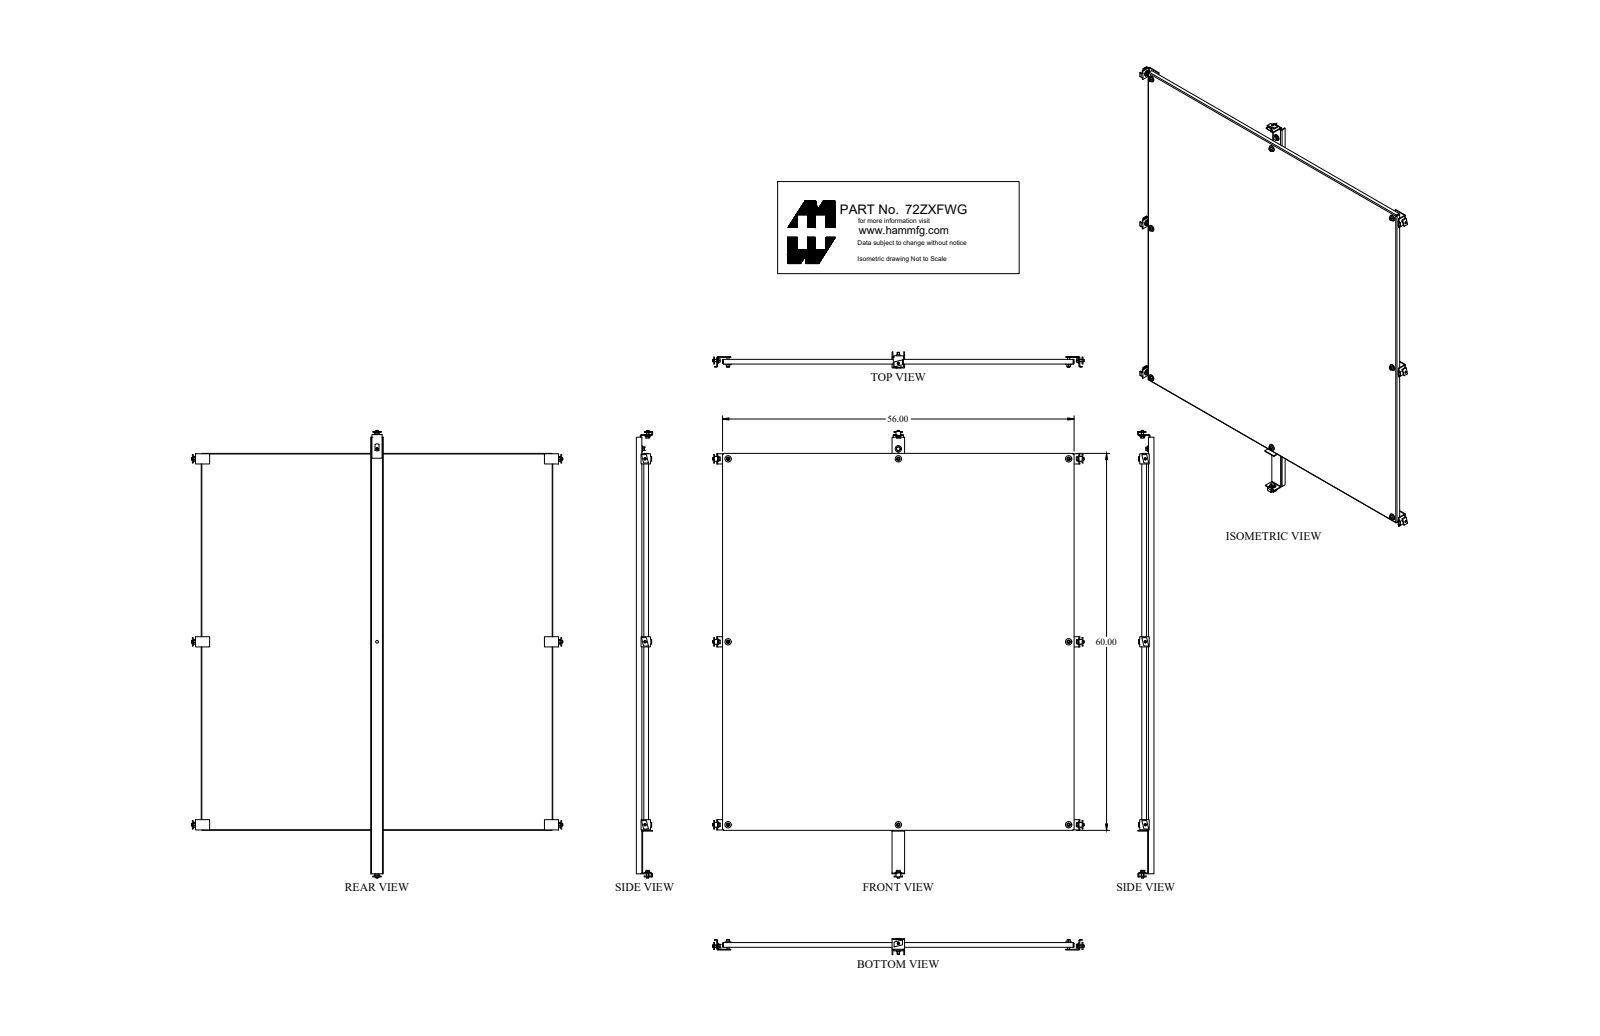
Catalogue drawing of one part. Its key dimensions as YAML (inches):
part_name: "72ZXFWG_Default"
step_written_by: "SolidWorks 2018 (CONFIG_CONTROL_DESIGN)"
units: inches
bodies: {solids: 18, faces: 385, planar: 188, cylindrical: 133, other: 64}
overall_size: [70.906, 58.582, 2.593]
volume: 371.4
surface_area: 7677
round_holes:
  - {diameter: 0.563, count: 8}
  - {diameter: 0.437, count: 5}
  - {diameter: 0.437, count: 1}
  - {diameter: 0.453, count: 1}
round_bosses_or_shafts:
  - {diameter: 0.65, count: 8}
  - {diameter: 0.33, count: 8}
  - {diameter: 0.375, count: 6}
  - {diameter: 0.375, count: 2}
partial_cylinders:
  - {radius: 0.06, count: 11}
  - {radius: 0.185, count: 11}
  - {radius: 0.048, count: 4}
  - {radius: 0.143, count: 4}
  - {radius: 0.219, count: 2}
face_to_face_distances: [0.095, 0.125, 1.187, 1.062, 0.967, 1.092, 26.905, 28.905, 27, 29]
hole_center_spacings: [39.8, 27.125, 29.125, 61.573, 64.256, 54.25, 58.25, 29.13]
